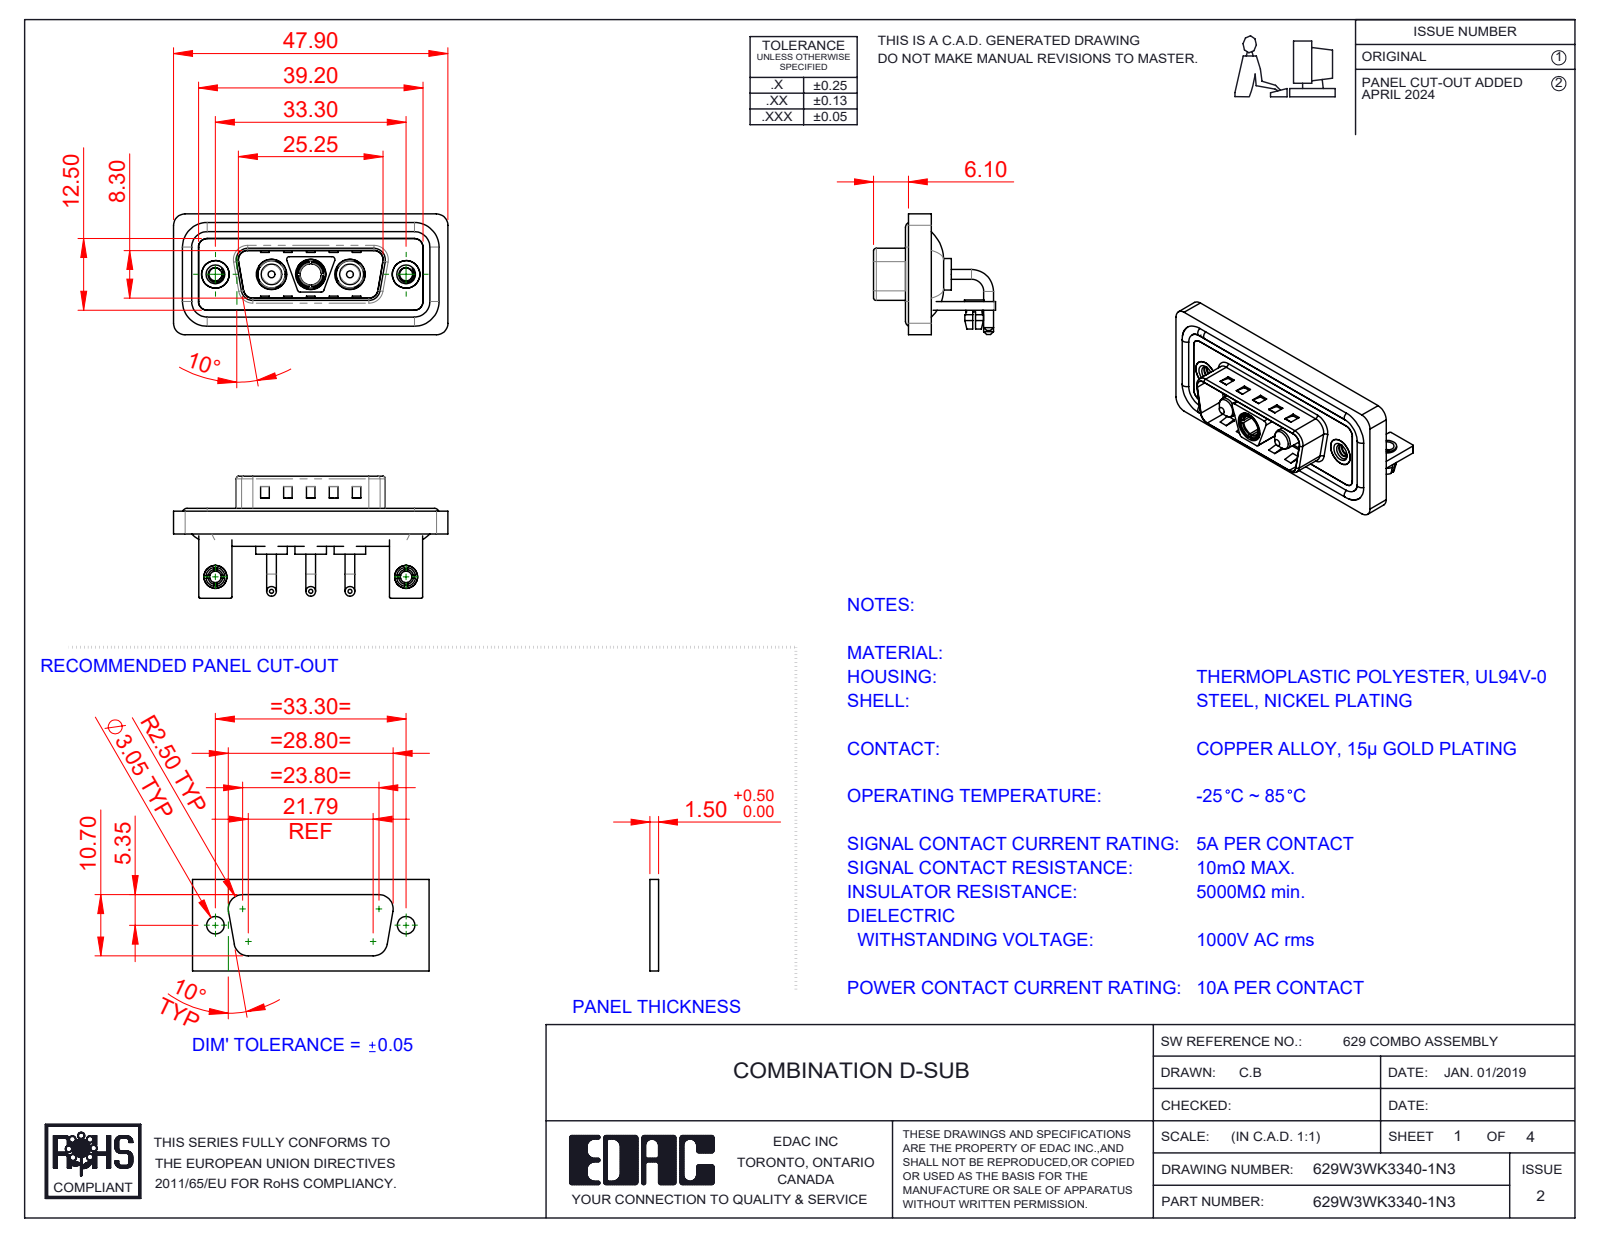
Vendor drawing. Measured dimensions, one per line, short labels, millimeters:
name: 629Combo Shell Front_15 Contacts; 629Combo Waterproof Housing_15 Contacts; 629Combo Stabilizer Bracket; 629Combo Housing_3WK3 (+6 more)
written by: SolidWorks 2023 (CONFIG_CONTROL_DESIGN)
unit: mm
bodies: 17 solids, 753 faces (299 planar, 306 cylindrical, 148 other)
size: 47.9 × 21.3 × 21.1
volume: 6 022 mm³; area: 10 058 mm²
holes: 3× ⌀4.85, 3× ⌀5.3, 2× ⌀2, 2× ⌀2.26, 2× ⌀2.5, 2× ⌀3.2, 2× ⌀4, 2× ⌀4.8, 2× ⌀5, 1× ⌀3.7
bosses: 6× ⌀1.7, 4× ⌀1.6, 3× ⌀5.5, 3× ⌀5.2, 3× ⌀4.75, 3× ⌀3.75, 2× ⌀4.9, 2× ⌀4
rounds: 21× R2, 18× R1.5, 16× R0.25, 13× R0.5, 8× R1.6, 4× R0.6, 4× R0.65, 4× R0.9
face distances: 0.4, 1.5, 0.8, 2.9, 1.1, 2.1, 3.7, 1.6, 1.2, 4.5
hole spacings: 6.85, 9.8, 16.65, 23.5, 33.3, 13.7
